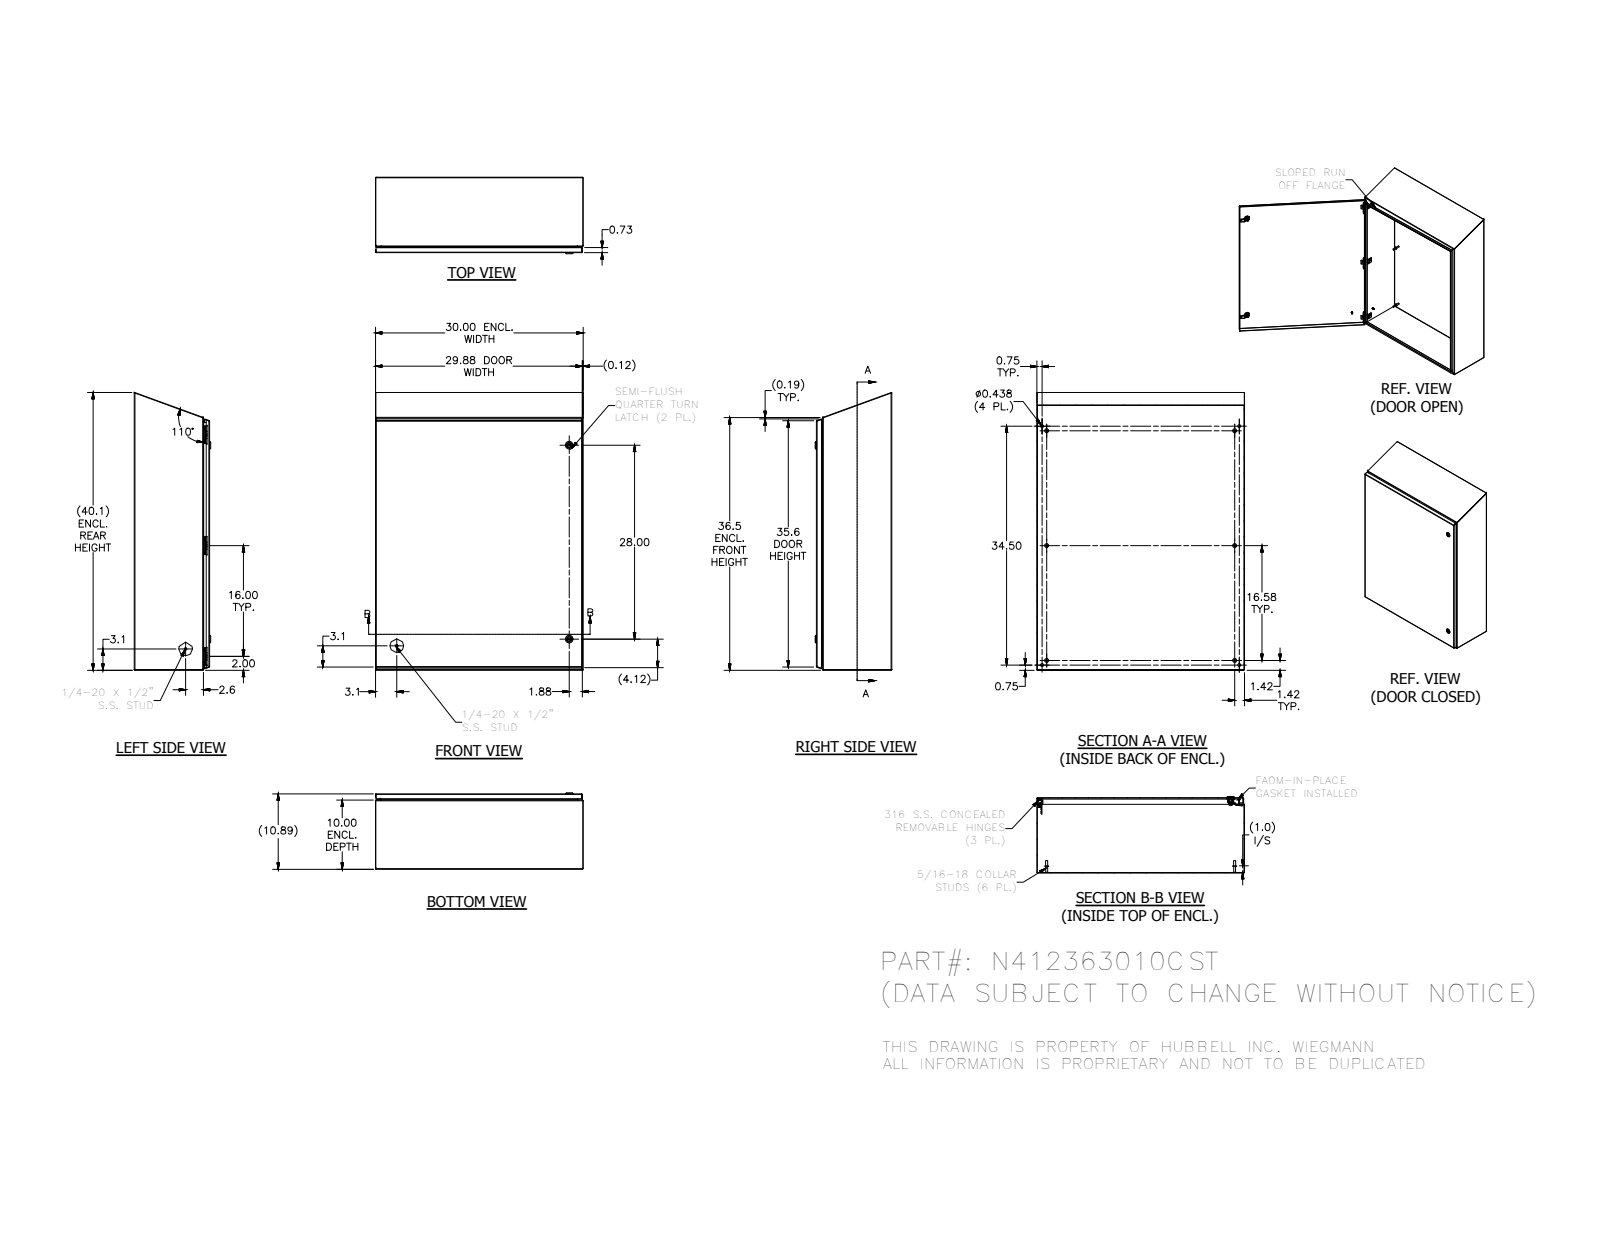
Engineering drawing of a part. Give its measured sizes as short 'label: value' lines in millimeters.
name: N412_CST-assm; N412363010CSTB3S; HFW3161; HFW328176 (+8 more)
written by: Autodesk Inventor 2012 (AUTOMOTIVE_DESIGN)
unit: mm
bodies: 51 solids, 2370 faces (900 planar, 872 cylindrical, 598 other)
size: 1019 × 762 × 280.5
volume: 4 783 000 mm³; area: 5 131 000 mm²
holes: 6× ⌀2.4, 6× ⌀3.9, 6× ⌀4.2, 6× ⌀4.4, 6× ⌀4.7, 4× ⌀4, 4× ⌀11.1, 2× ⌀5, 2× ⌀8, 2× ⌀10, 2× ⌀10.2, 2× ⌀16.1
bosses: 14× ⌀6.4, 6× ⌀14.3, 6× ⌀9.1, 6× ⌀8.1, 6× ⌀7.6, 6× ⌀7, 6× ⌀6.5, 6× ⌀4.2
rounds: 54× R0.3, 38× R1.3, 33× R0.8, 26× R0.4, 24× R3.2, 23× R0.5, 19× R2.7, 12× R0.8
face distances: 1.9, 274.7, 272.8, 276.5, 760.1, 758.2, 762, 252.1, 22.5, 20.7
hole spacings: 406.4, 812.8, 406.6, 12.7, 16.7, 16.8, 33.2, 33.3
